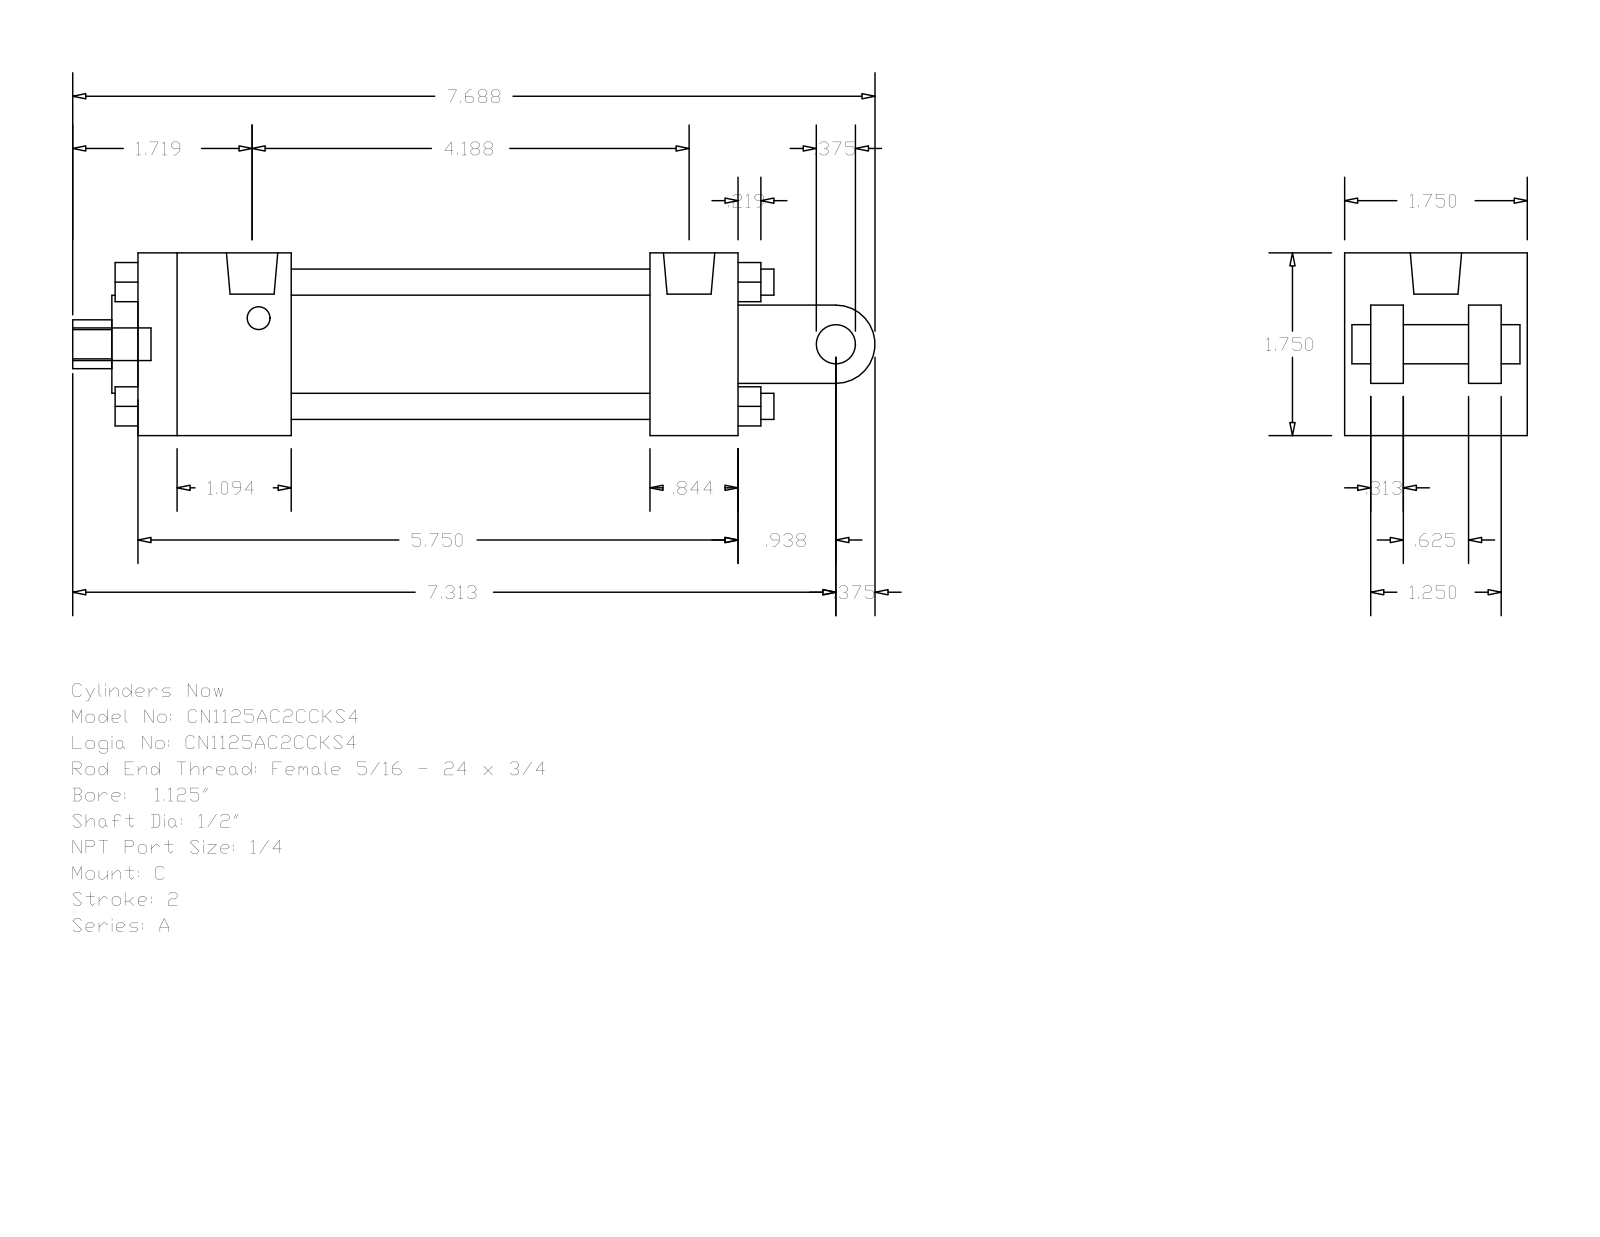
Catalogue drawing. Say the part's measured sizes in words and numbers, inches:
The part is named "A_C__0112_0.5". Its 3-D file was written by "GSSL Pune (CONFIG_CONTROL_DESIGN)". It is 0 solids with 135 faces: 102 planar, 33 cylindrical and 0 other. Overall it measures 7.687 by 1.75 by 1.75 inches. Round holes: 2 of diameter 0.219, 1 of diameter 0.492, 1 of diameter 0.5, 1 of diameter 0.937, 1 of diameter 1.255. Round bosses or shafts: 4 of diameter 0.25, 2 of diameter 0.219, 1 of diameter 0.492, 1 of diameter 0.375, 1 of diameter 0.313. Partial cylindrical surfaces (rounded edges, fillets, slot ends): 1 of radius 0.234, 1 of radius 0.375. The main face-to-face distances are 1.75, 0.25, 1.25, 0.563, 5.75, 1.188, 4.906, 0.844, 1.469, 3.437. The hole center spacings are 0.063.
